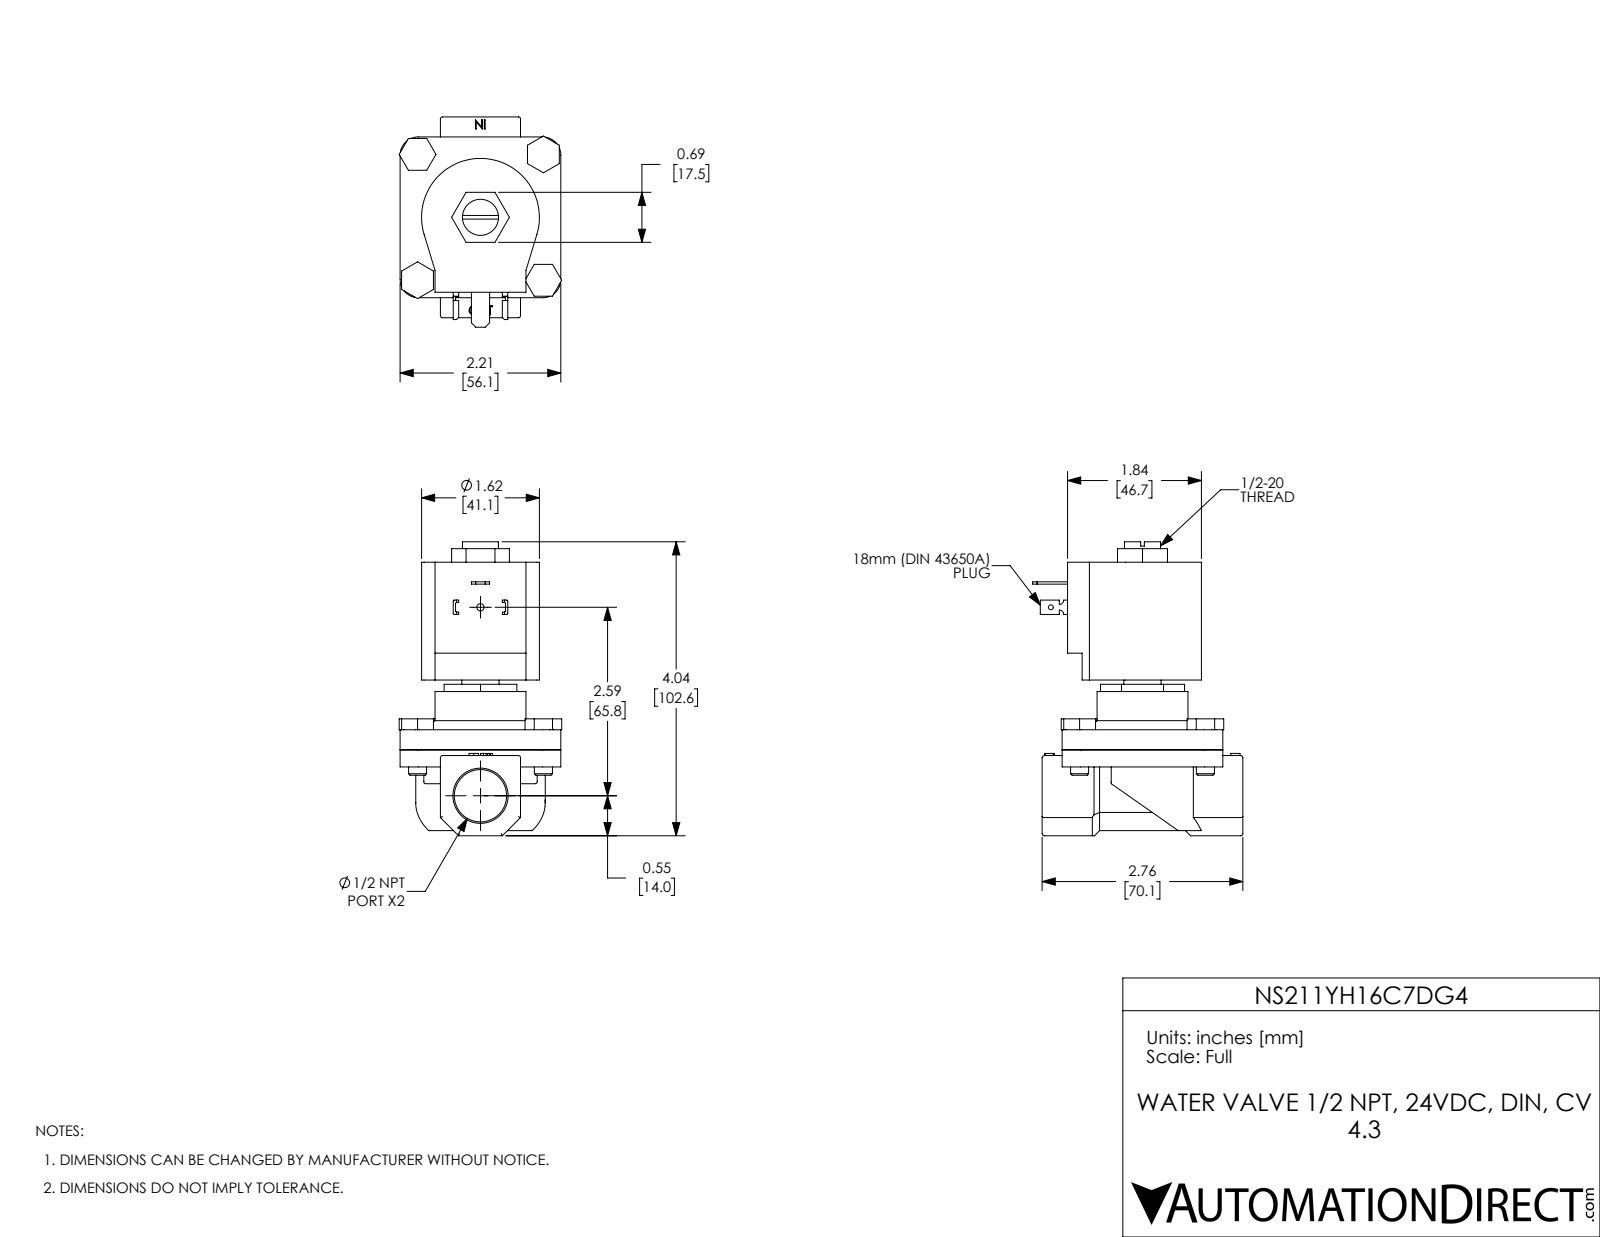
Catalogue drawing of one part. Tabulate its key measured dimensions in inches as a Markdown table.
| quantity | value |
| --- | --- |
| part name | NS211YH16C7DG4 |
| STEP written by | SolidWorks 2024 (CONFIG_CONTROL_DESIGN) |
| units | inches |
| bodies | 11 solids, 330 faces (196 planar, 99 cylindrical, 35 other) |
| overall size | 4.04 × 2.89 × 2.235 |
| volume | 9.828 in³ |
| surface area | 63.56 in² |
| round holes (diameter × count) | 0.25 × 4, 0.067 × 1, 0.1 × 1, 0.496 × 1, 0.512 × 1, 0.719 × 1, 1.155 × 1 |
| round bosses / shafts (diameter × count) | 0.248 × 4, 1.25 × 1 |
| partial cylindrical surfaces (radius × count) | 0.03 × 15, 0.015 × 8, 0.25 × 4, 0.06 × 2, 0.81 × 1, 0.89 × 1 |
| main face-to-face distances | 0.276, 2.579, 2.303, 0.554, 1.656, 0.236, 0.512, 2.815, 2.21, 1.102 |
| hole center spacings | 1.223, 1.73, 2.446, 2.59 |
